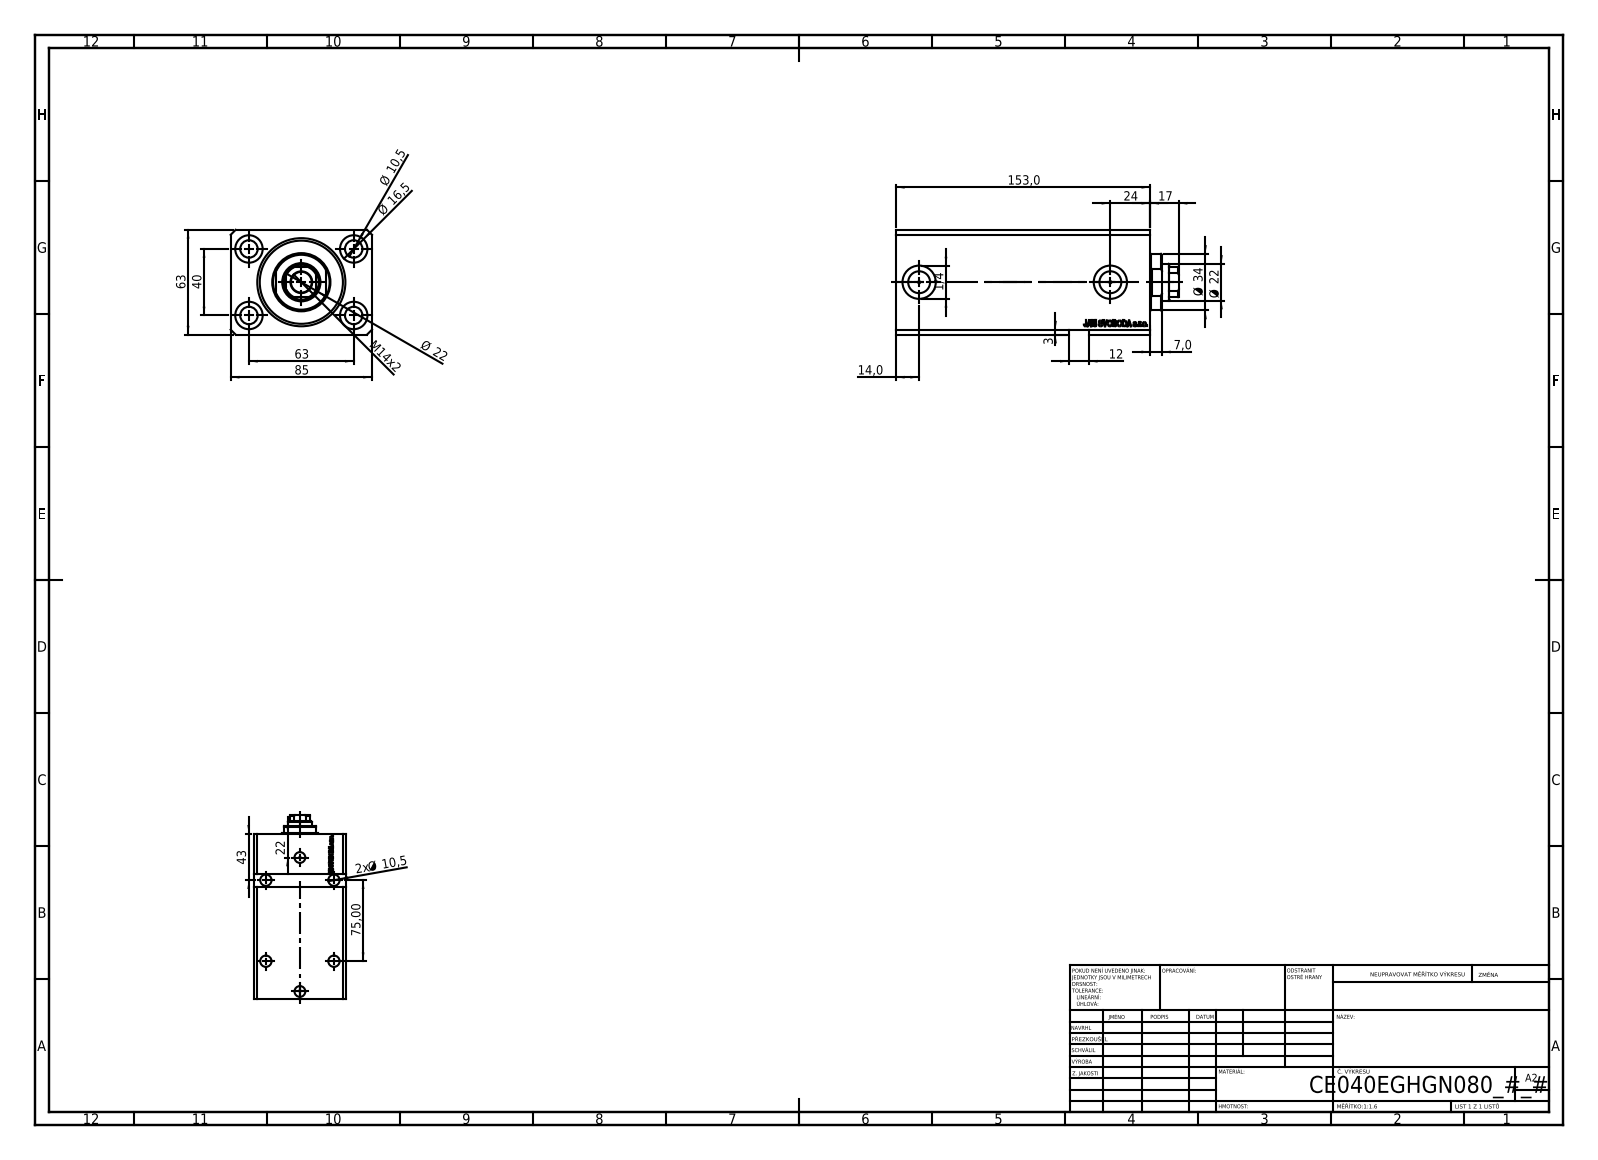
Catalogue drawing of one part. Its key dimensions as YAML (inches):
part_name: "V250CE_E_Body; V250CE_VC_E; V250CE_C_VCP"
step_written_by: "SolidWorks 2019 (CONFIG_CONTROL_DESIGN)"
units: inches
bodies: {solids: 3, faces: 937, planar: 459, cylindrical: 104, other: 374}
overall_size: [6.693, 3.346, 2.48]
volume: 40.65
surface_area: 195.7
round_holes:
  - {diameter: 0.413, count: 8}
  - {diameter: 0.049, count: 4}
  - {diameter: 0.65, count: 4}
  - {diameter: 0.394, count: 2}
  - {diameter: 0.518, count: 2}
  - {diameter: 0.787, count: 2}
  - {diameter: 0.492, count: 1}
  - {diameter: 0.866, count: 1}
  - {diameter: 1.575, count: 1}
  - {diameter: 2.087, count: 1}
round_bosses_or_shafts:
  - {diameter: 1.339, count: 1}
partial_cylinders:
  - {radius: 0.413, count: 1}
face_to_face_distances: [2.48, 3.346, 6.024, 0.669, 5.354, 0.449, 4.906, 5.575, 2.205, 2.362]
hole_center_spacings: [1.469, 2.48, 1.491, 1.575, 1.646, 1.659, 2.938, 2.953]
